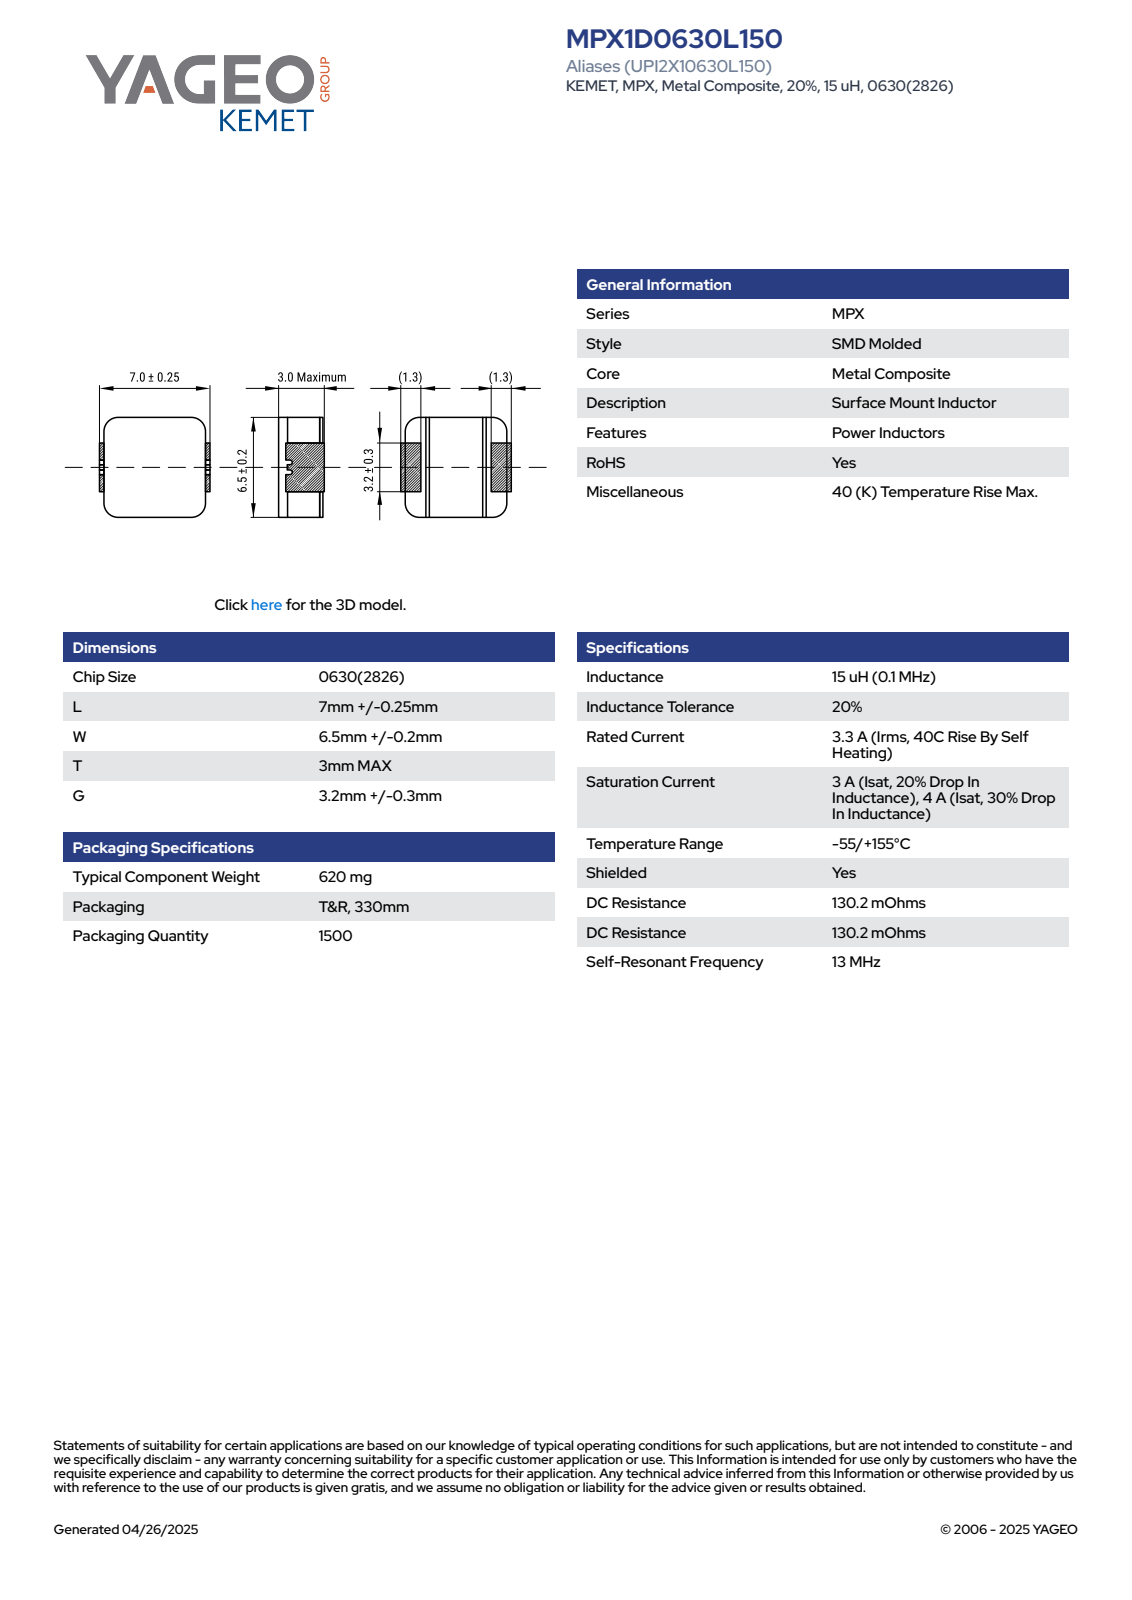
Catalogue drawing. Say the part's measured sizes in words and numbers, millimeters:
The part is named "MPX1D0630M(KEMET)". Its 3-D file was written by "SolidWorks 2018 (AUTOMOTIVE_DESIGN)". It is 1 solid with 138 faces: 117 planar, 21 cylindrical and 0 other. Overall it measures 7.25 by 6.7 by 3.06 millimeters. Its volume is 135 cubic millimeters and its surface area 198 square millimeters. Partial cylindrical surfaces (rounded edges, fillets, slot ends): 4 of radius 0.21, 4 of radius 0.99, 4 of radius 1, 3 of radius 0.15. The main face-to-face distances are 6.7, 3, 6.98, 7, 6.72, 2.85, 3.06, 7.26, 6.74, 1.6.
